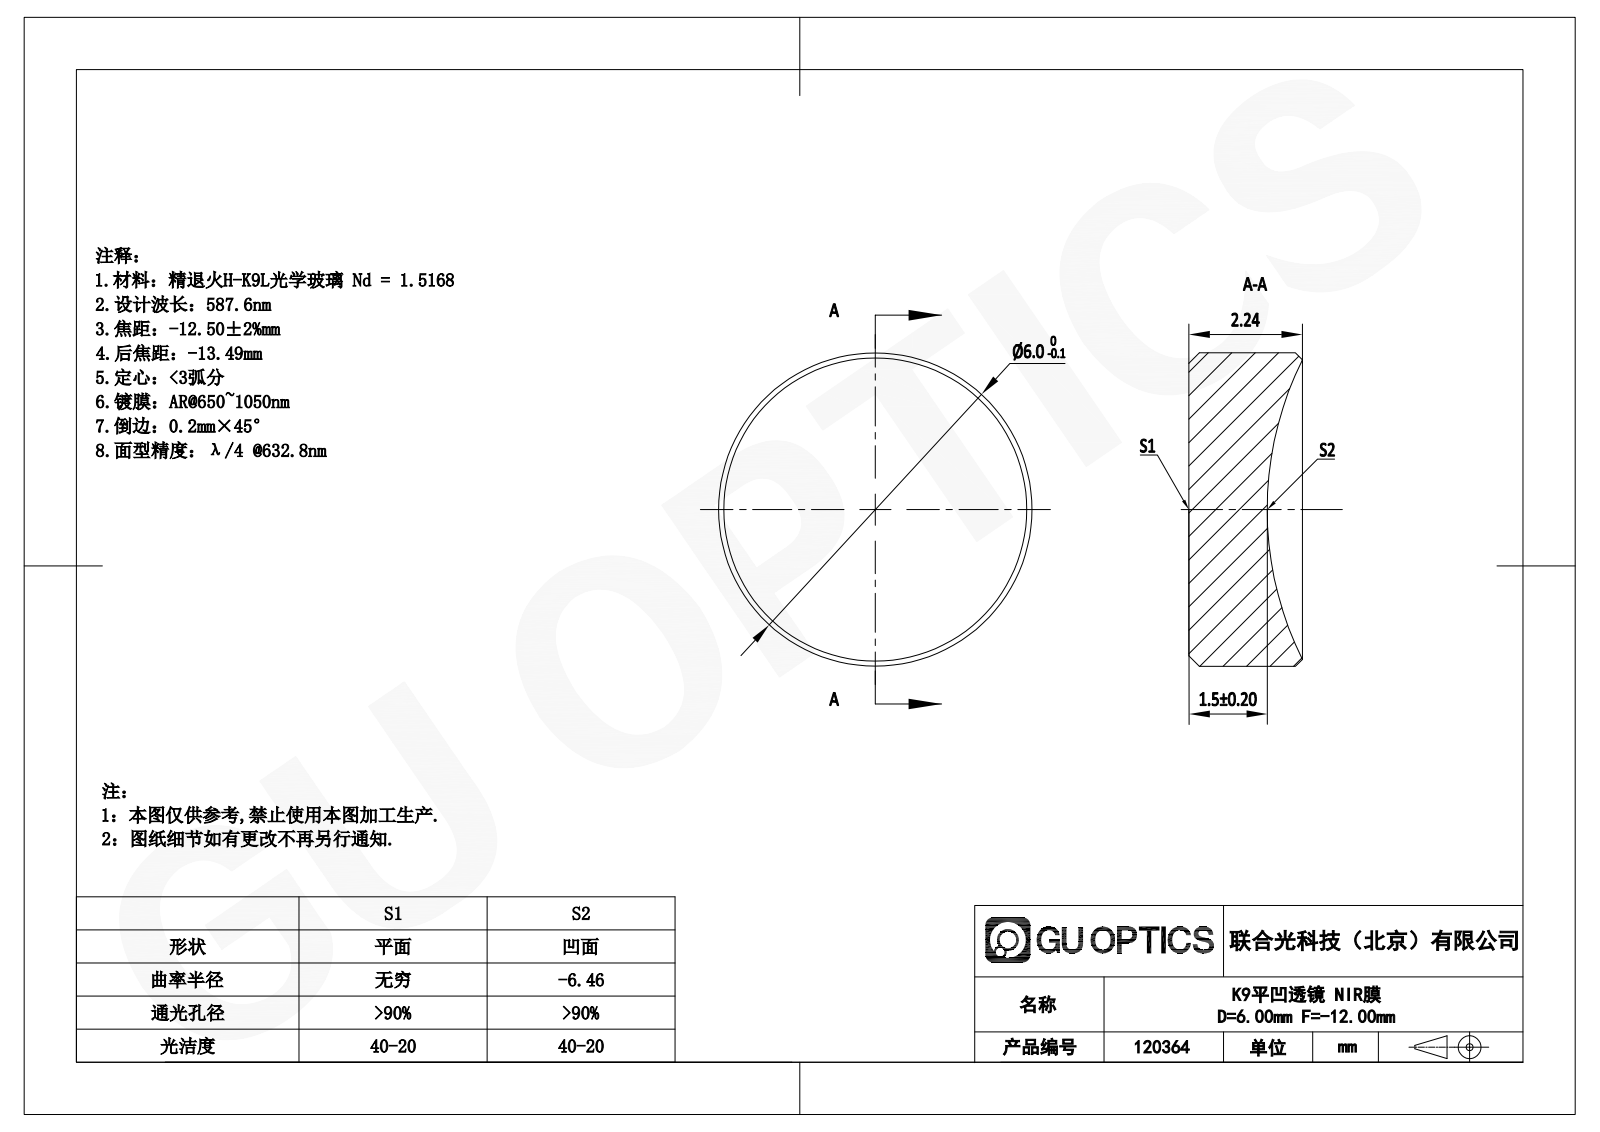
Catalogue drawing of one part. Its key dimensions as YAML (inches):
part_name: "GL13-006A-012"
step_written_by: "SolidWorks 2022 (AUTOMOTIVE_DESIGN)"
units: inches
bodies: {solids: 1, faces: 9, planar: 1, cylindrical: 2, other: 6}
overall_size: [0.236, 0.236, 0.085]
volume: 0.003
surface_area: 0.15
round_bosses_or_shafts:
  - {diameter: 0.236, count: 1}
